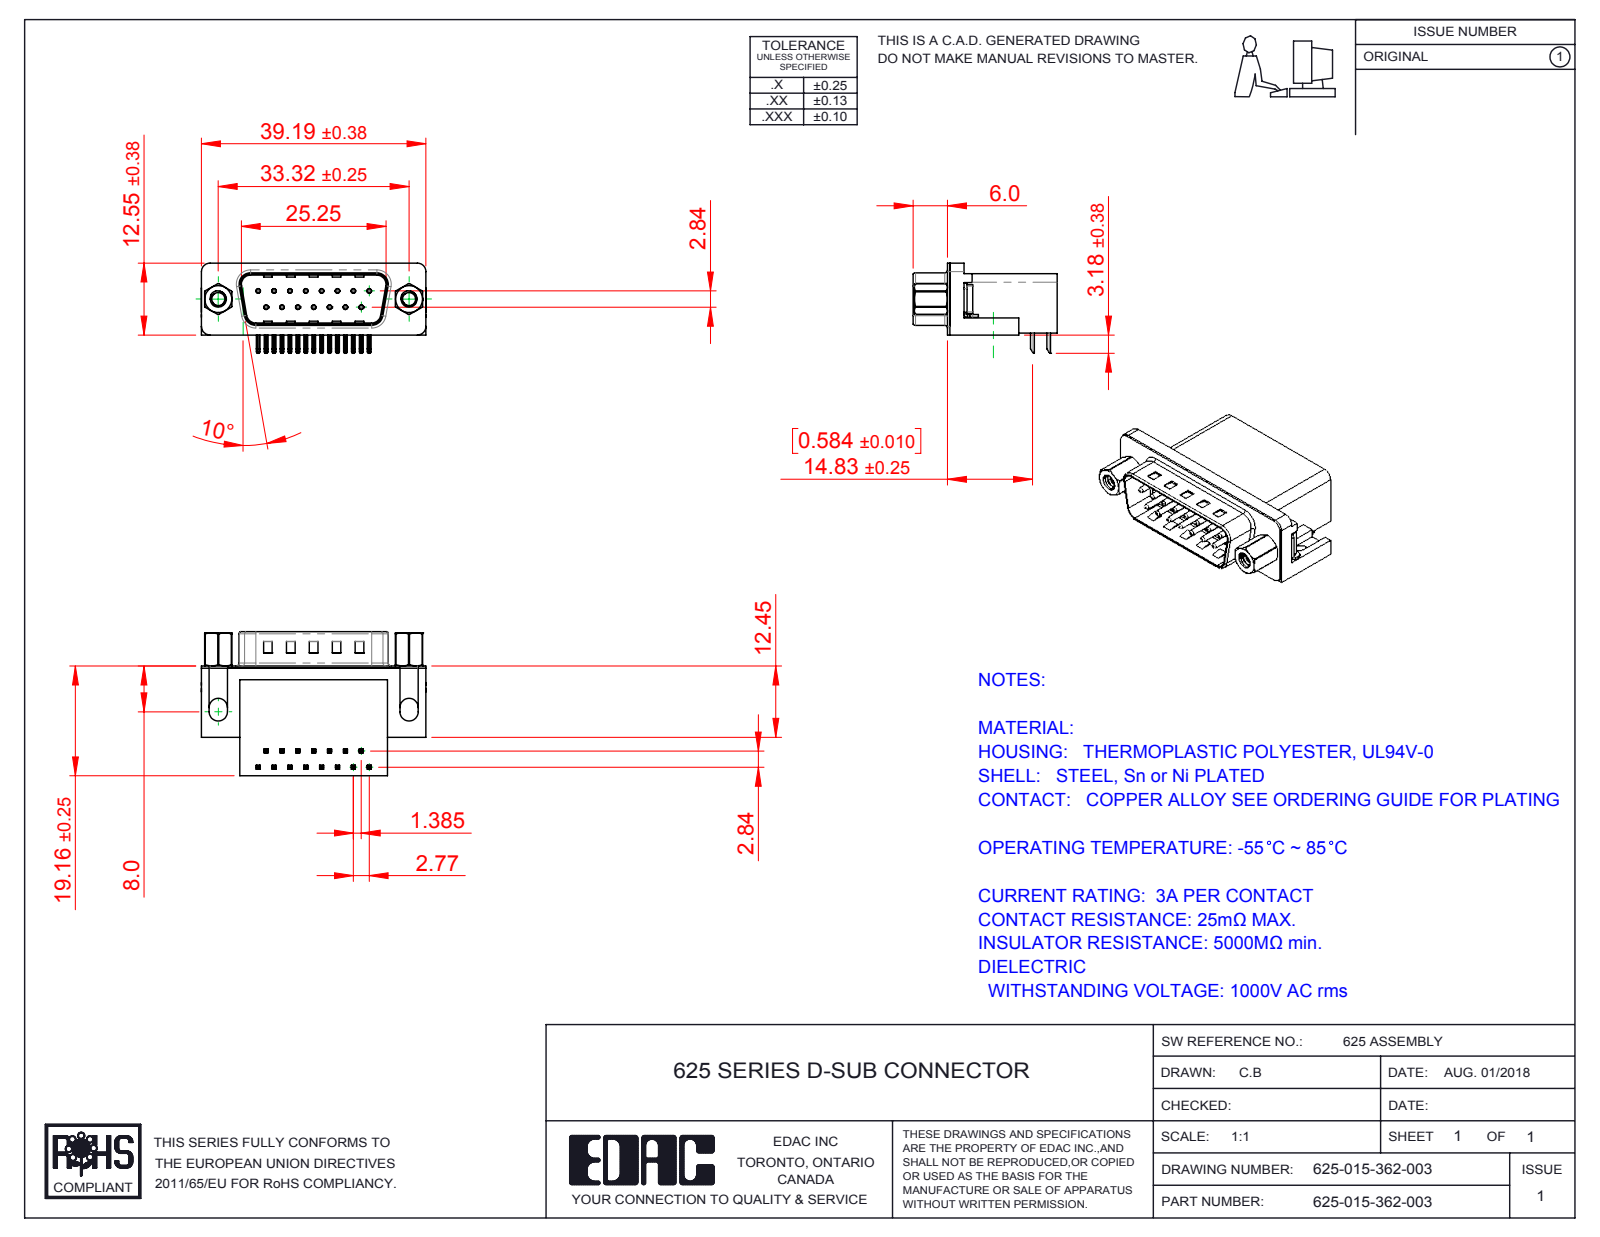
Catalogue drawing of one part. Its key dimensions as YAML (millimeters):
part_name: "625-015-362-003; 625 4-40 Hex Standoff 5; 625 Housing_15 Socket; 625 Shell_15 Socket (+4 more)"
step_written_by: "SolidWorks 2016 (CONFIG_CONTROL_DESIGN)"
units: millimeters
bodies: {solids: 23, faces: 1603, planar: 917, cylindrical: 515, other: 171}
overall_size: [39.22, 25.16, 15.73]
volume: 6429
surface_area: 6773
round_holes:
  - {diameter: 0.35, count: 15}
  - {diameter: 0.8, count: 15}
  - {diameter: 2.26, count: 2}
  - {diameter: 2.29, count: 2}
  - {diameter: 4, count: 2}
  - {diameter: 4.8, count: 2}
  - {diameter: 5, count: 2}
round_bosses_or_shafts:
  - {diameter: 0.75, count: 15}
  - {diameter: 4.9, count: 2}
  - {diameter: 4.75, count: 2}
  - {diameter: 3.9, count: 2}
  - {diameter: 2.79, count: 2}
partial_cylinders:
  - {radius: 0.25, count: 68}
  - {radius: 0.12, count: 30}
  - {radius: 1, count: 16}
  - {radius: 0.5, count: 9}
  - {radius: 1.6, count: 8}
  - {radius: 1.5, count: 6}
  - {radius: 0.9, count: 4}
  - {radius: 2, count: 4}
face_to_face_distances: [0.4, 10.35, 18.76, 2.1, 19.16, 10.46, 1.7, 10.86, 8.76, 16.26]
hole_center_spacings: [3.16, 2.77, 5.54, 8.31, 11.08, 5.03, 5.04, 7.48]
